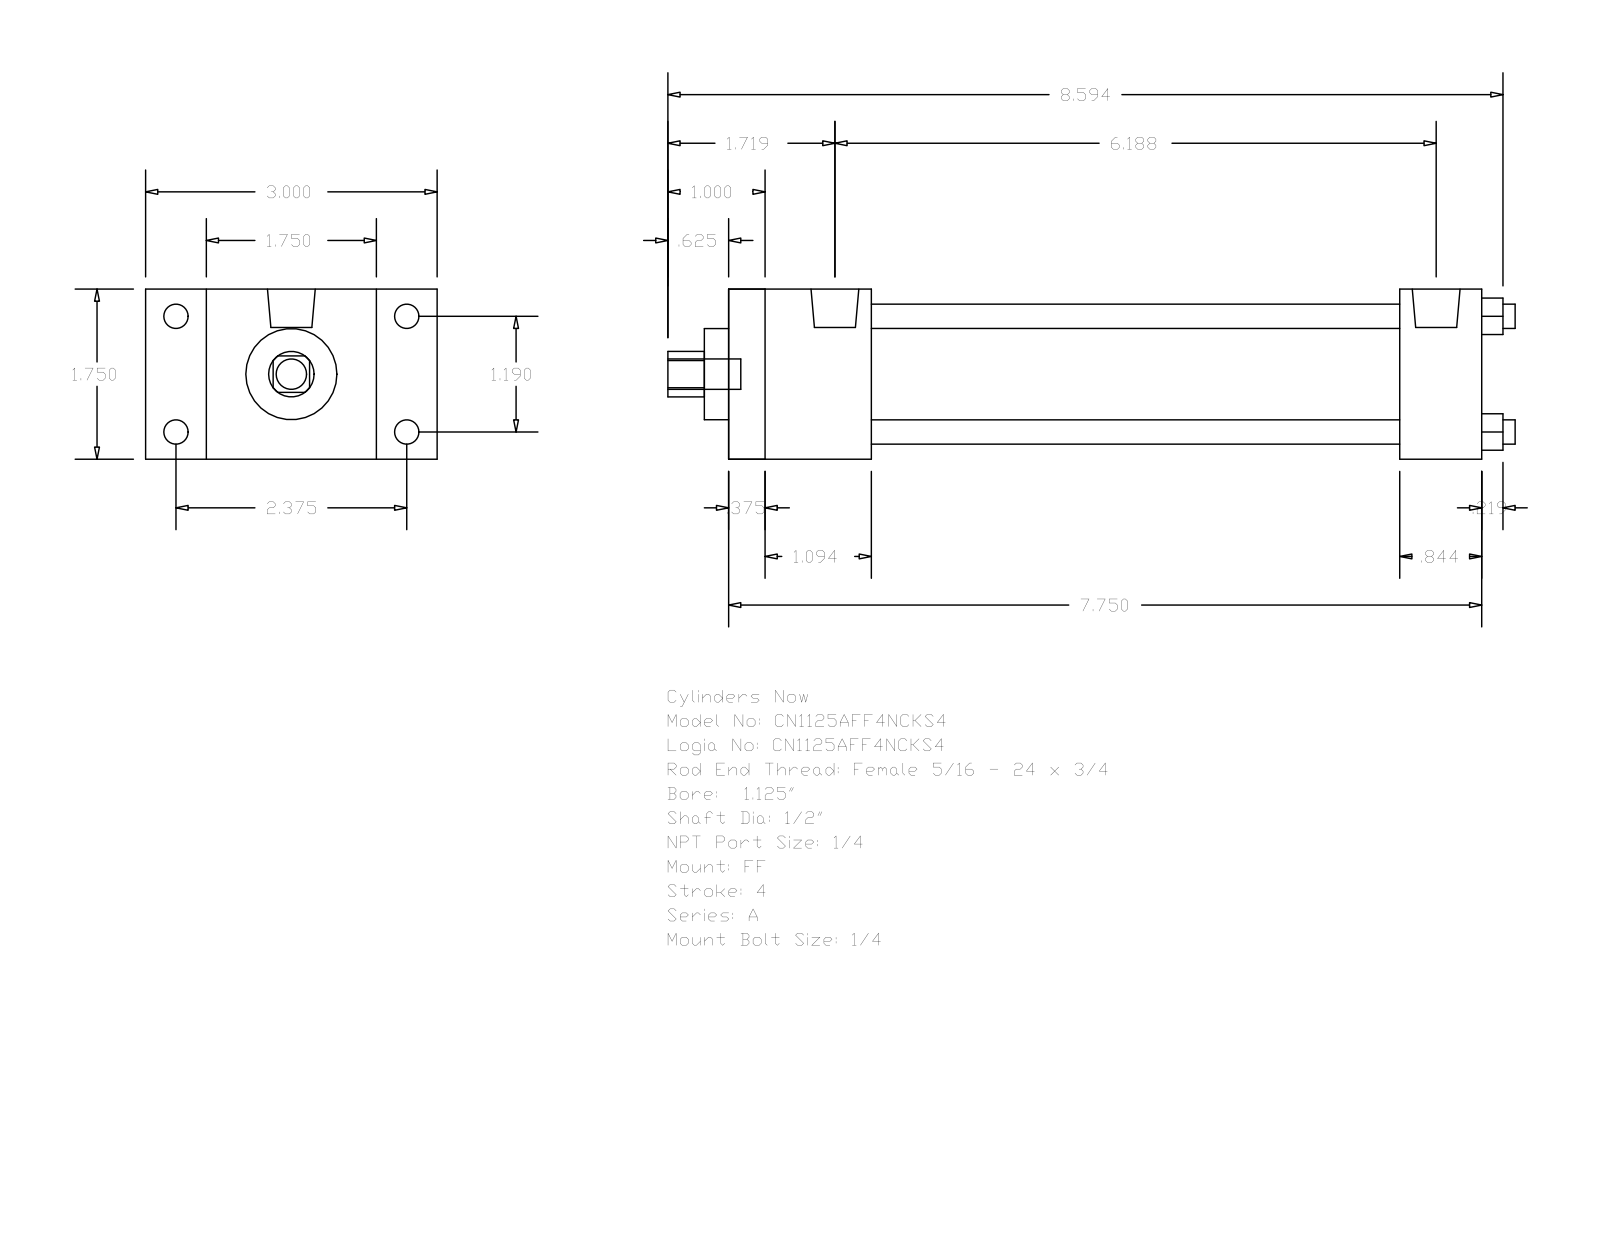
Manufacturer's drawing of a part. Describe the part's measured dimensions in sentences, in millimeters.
The part is named "A_FF__0112_0.5". Its 3-D file was written by "GSSL Pune (CONFIG_CONTROL_DESIGN)". It is 0 solids with 92 faces: 64 planar, 28 cylindrical and 0 other. Overall it measures 221.46 by 76.2 by 44.45 millimeters. Round holes: 4 of diameter 6.35, 1 of diameter 12.7, 1 of diameter 23.81, 1 of diameter 31.88. Round bosses or shafts: 4 of diameter 6.35, 4 of diameter 5.56, 2 of diameter 12.49, 1 of diameter 7.94. Partial cylindrical surfaces (rounded edges, fillets, slot ends): 1 of radius 5.94. The main face-to-face distances are 44.46, 196.84, 9.52, 187.32, 15.87, 175.41, 165.89, 21.43, 37.3, 27.78. The hole center spacings are 21.37, 30.22, 42.74.
